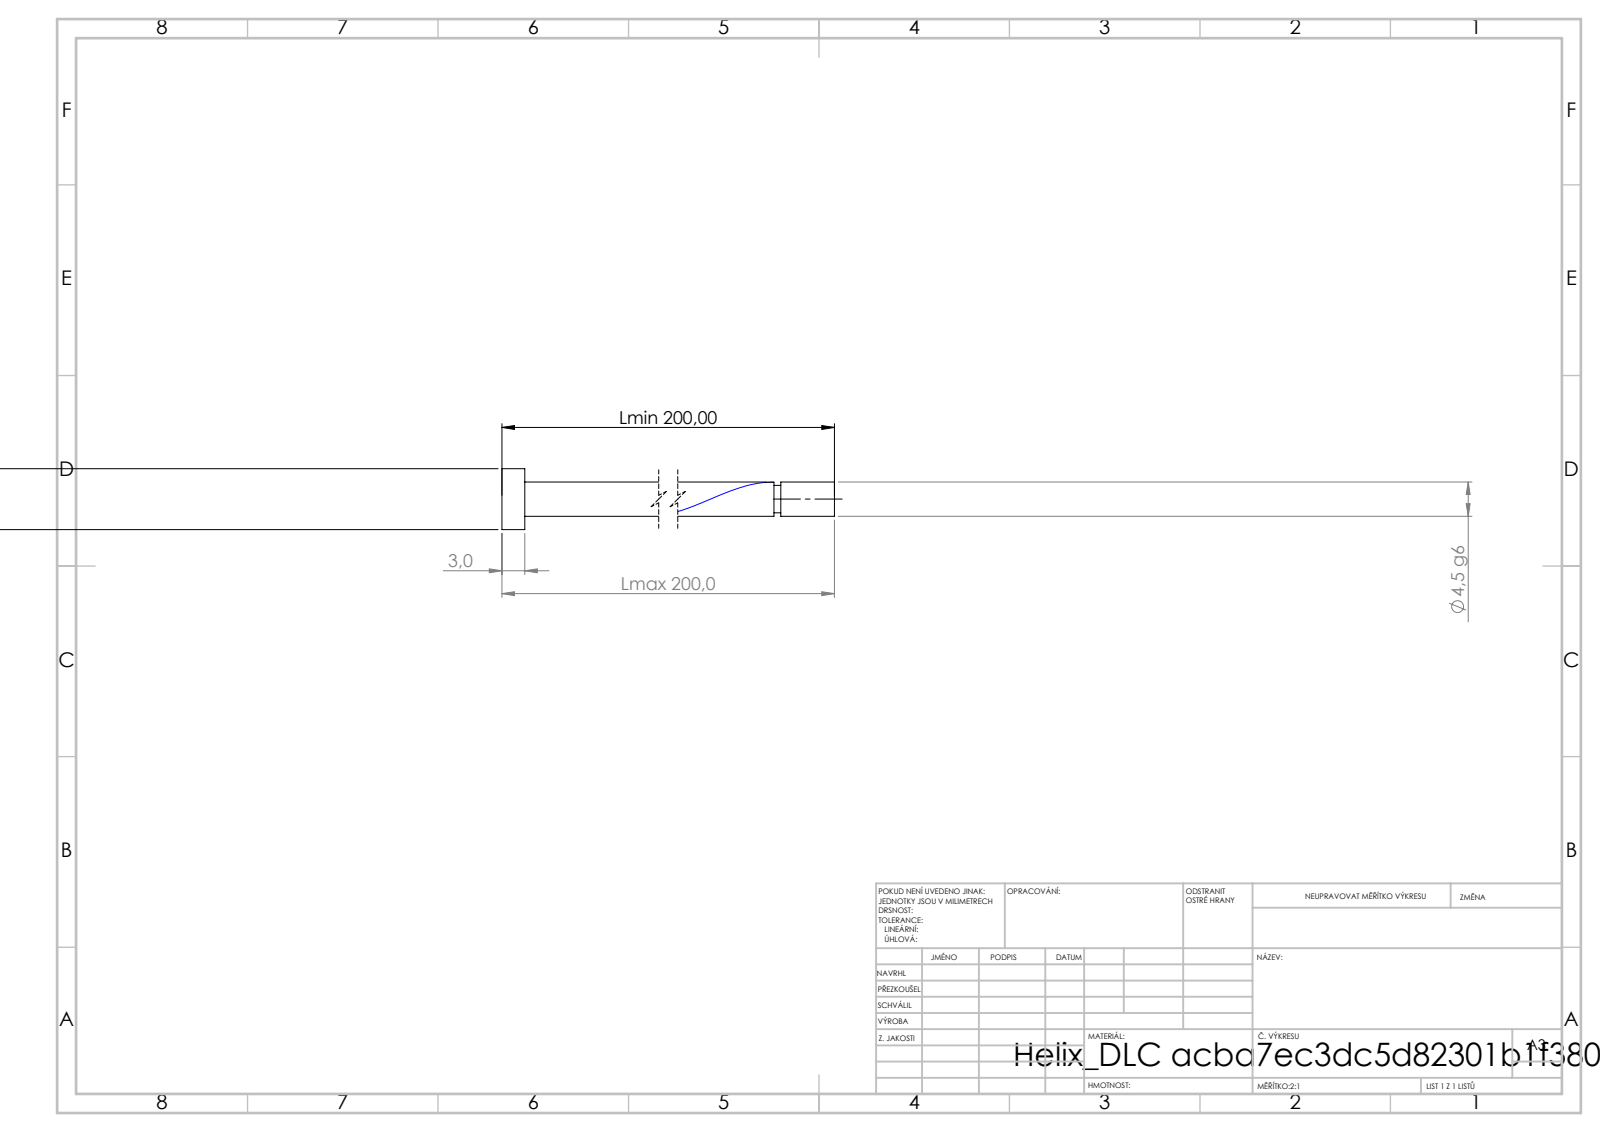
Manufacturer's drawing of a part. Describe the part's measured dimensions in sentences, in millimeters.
Its 3-D file was written by "SolidWorks 2019 (CONFIG_CONTROL_DESIGN)". It is 1 solid with 21 faces: 6 planar, 14 cylindrical and 1 other. Overall it measures 200 by 8 by 8 millimeters. Its volume is 3 248 cubic millimeters and its surface area 3 017 square millimeters. Round bosses or shafts: 1 of diameter 8, 1 of diameter 4.5, 1 of diameter 3.6. The main face-to-face distances are 3, 200, 197, 192.96, 189.96, 7.04, 192.06, 189.06, 0.9, 7.94.
